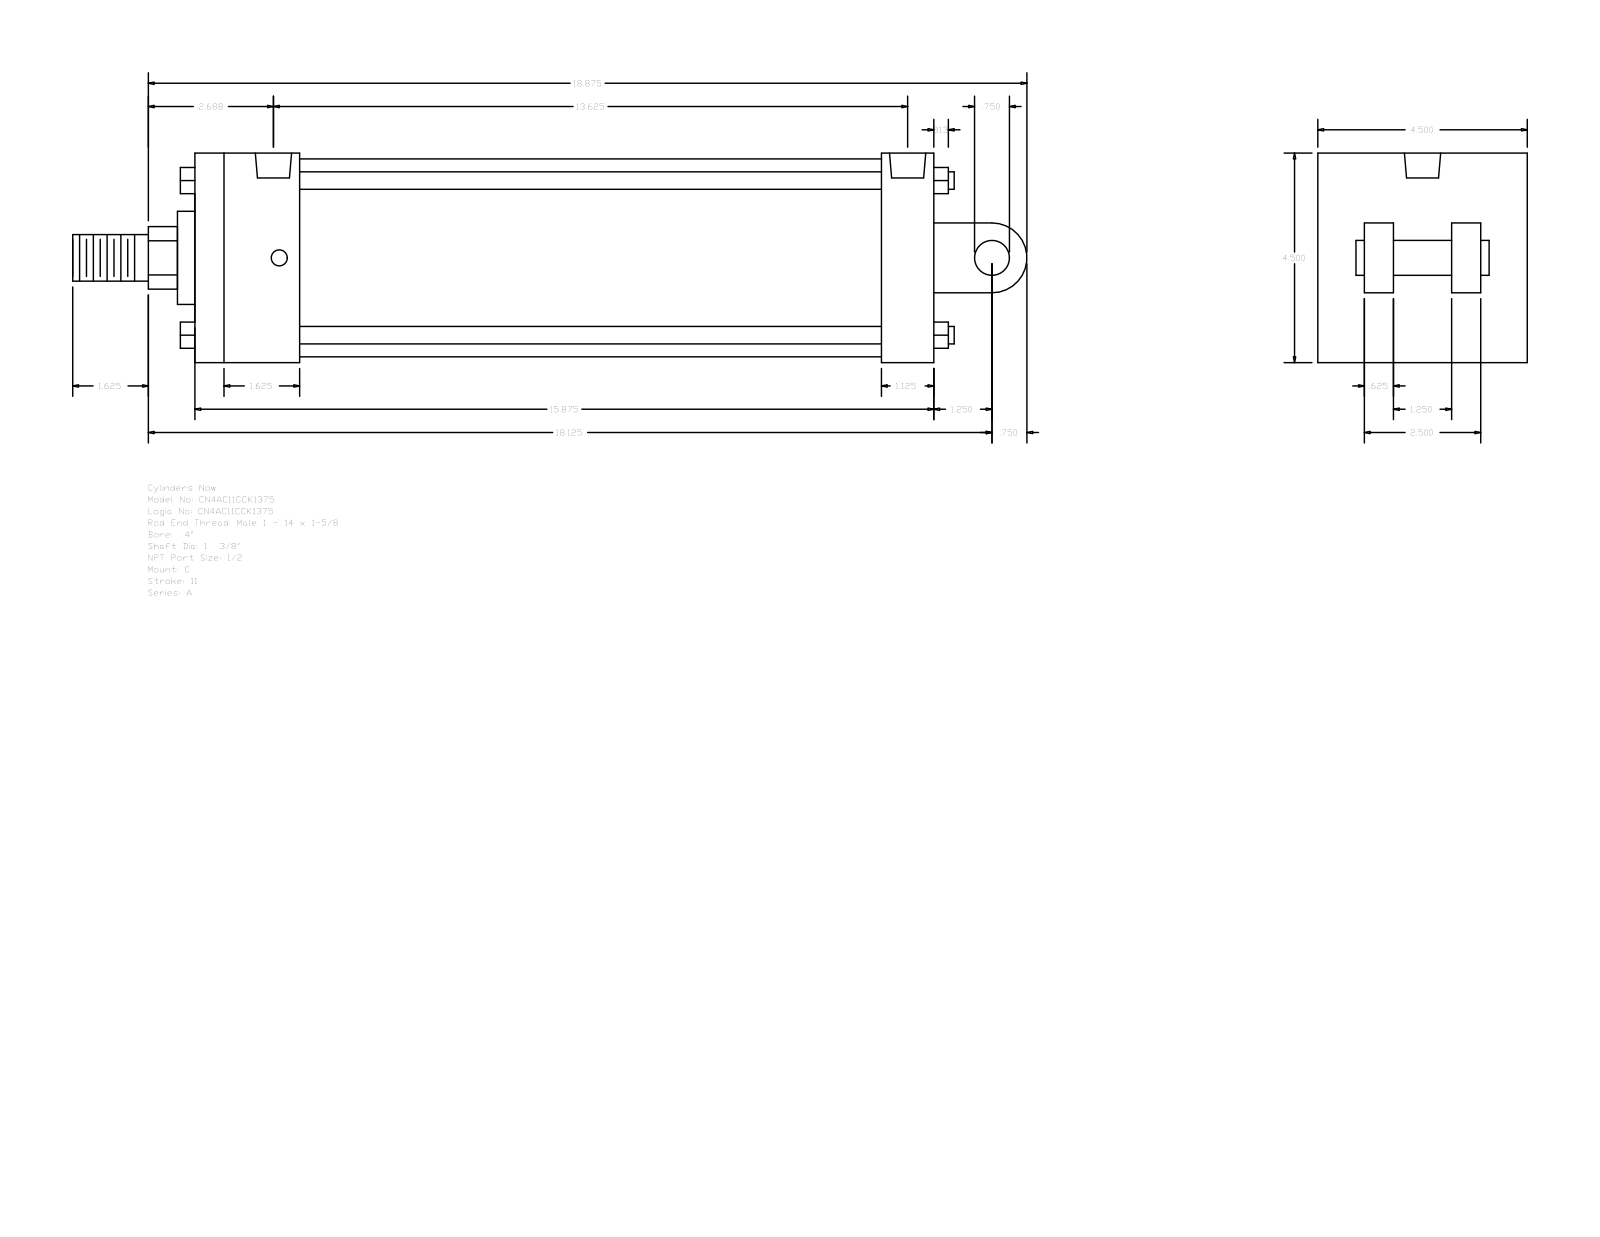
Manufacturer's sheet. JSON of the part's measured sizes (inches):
{"part_name": "A_C__0400_1.375", "step_written_by": "GSSL Pune (CONFIG_CONTROL_DESIGN)", "units": "inches", "bodies": {"solids": 0, "faces": 135, "planar": 102, "cylindrical": 33, "other": 0}, "overall_size": [20.5, 4.5, 4.5], "round_holes": [[0.344, 4], [0.778, 2]], "round_bosses_or_shafts": [[0.375, 4], [4.25, 1], [2, 1], [1.375, 1], [1, 1], [0.75, 1]], "partial_cylinders_radius": [[0.672, 1], [0.75, 1]], "face_to_face_distances": [4.5, 15.875, 2.25, 2.875, 14.75, 1.125, 12.5, 13.625, 1.625, 1], "hole_center_spacings": [0.125, 13.375, 13.5, 13.625]}
